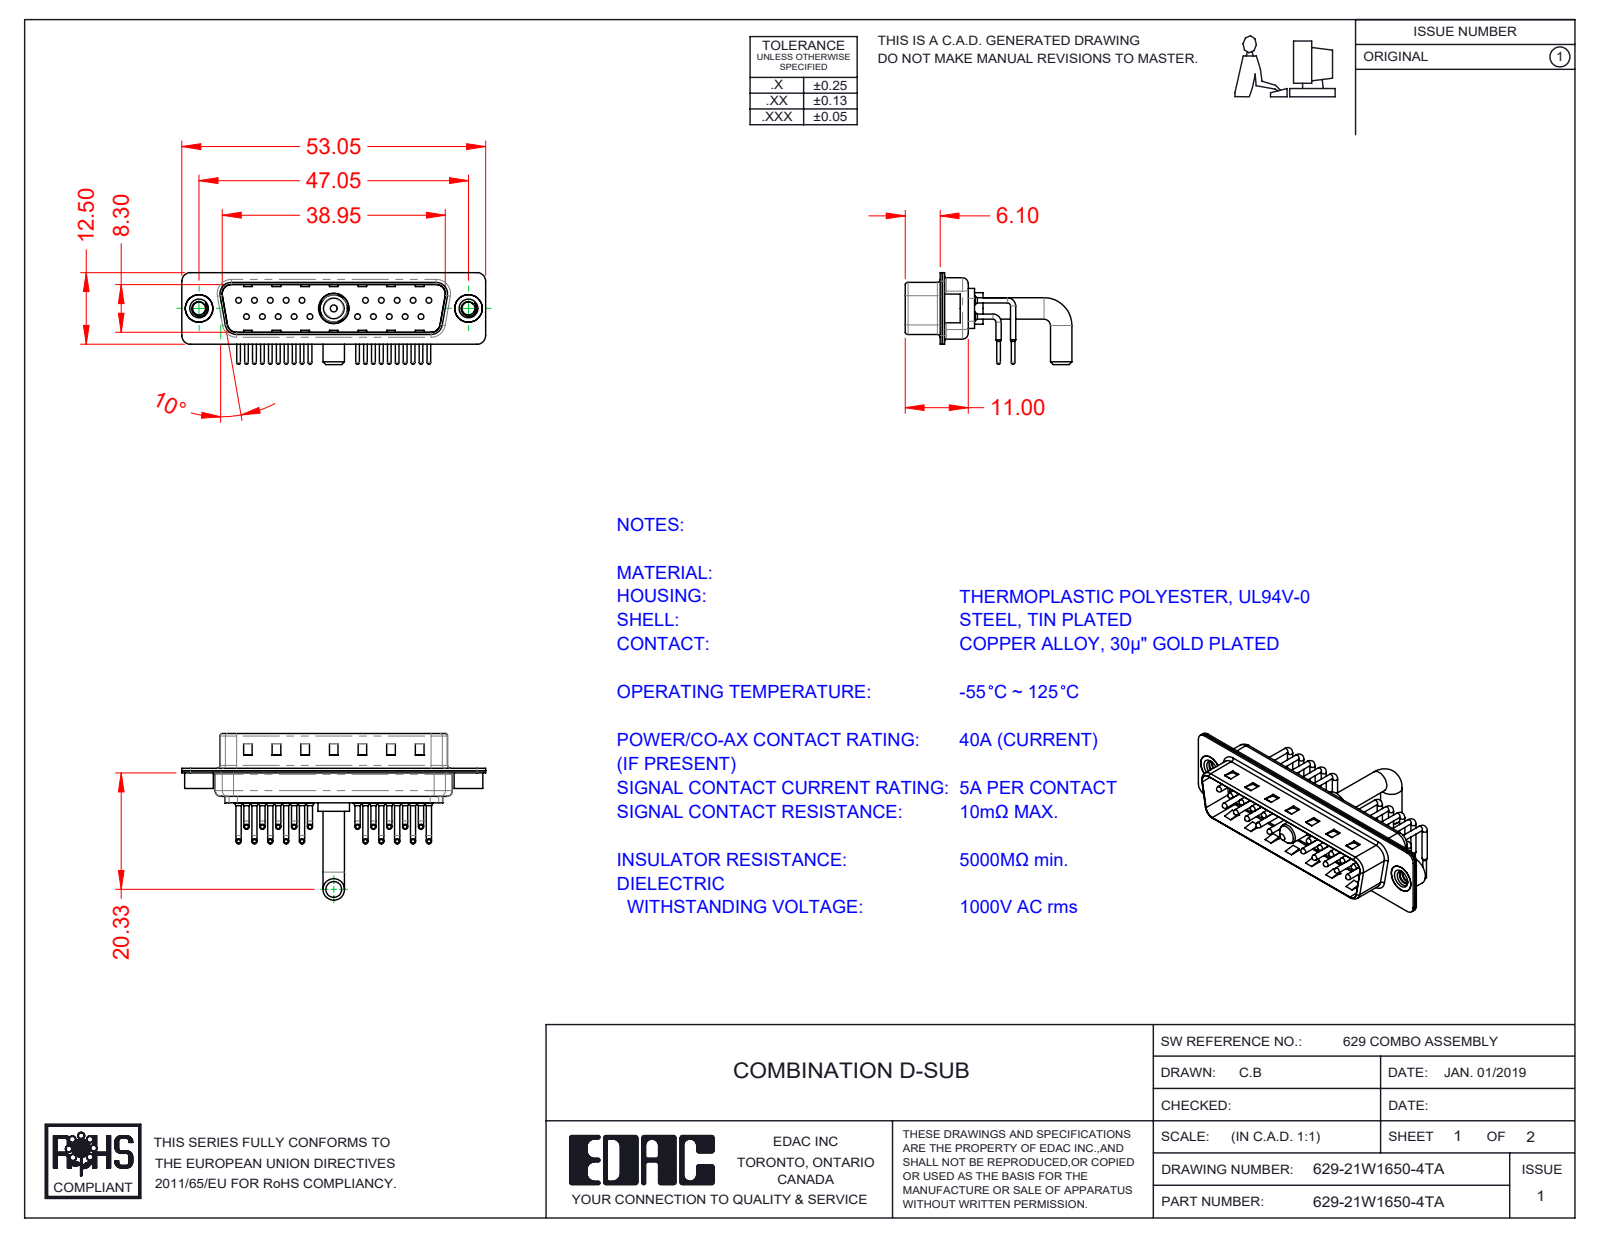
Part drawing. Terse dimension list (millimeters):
name: 629Combo Shell Rear_25 Contacts; 629Combo Threaded Rivet_2; 629Combo Contact Row 1; 629Combo Shell Front_25 Contacts (+4 more)
written by: SolidWorks 2020 (CONFIG_CONTROL_DESIGN)
unit: mm
bodies: 27 solids, 2619 faces (1461 planar, 878 cylindrical, 280 other)
size: 53.05 × 29.11 × 16.05
volume: 3 170 mm³; area: 7 723 mm²
holes: 20× ⌀0.75, 20× ⌀1.6, 20× ⌀2, 2× ⌀2.26, 2× ⌀4, 2× ⌀4.8, 1× ⌀4.85, 1× ⌀5.3
bosses: 40× ⌀0.9, 20× ⌀1.5, 20× ⌀1, 20× ⌀0.65, 2× ⌀5, 2× ⌀4.9, 2× ⌀3.75, 1× ⌀5.5
rounds: 20× R1.01, 16× R1.5, 12× R2, 8× R0.5, 8× R1.6, 4× R0.25, 4× R0.6, 4× R0.65
face distances: 0.4, 0.8, 9.5, 9.1, 8.7, 9.9, 0.75, 1.2, 0.35, 5.6
hole spacings: 3.16, 2.77, 5.54, 8.31, 5.04, 19.39, 20.97, 22.16
